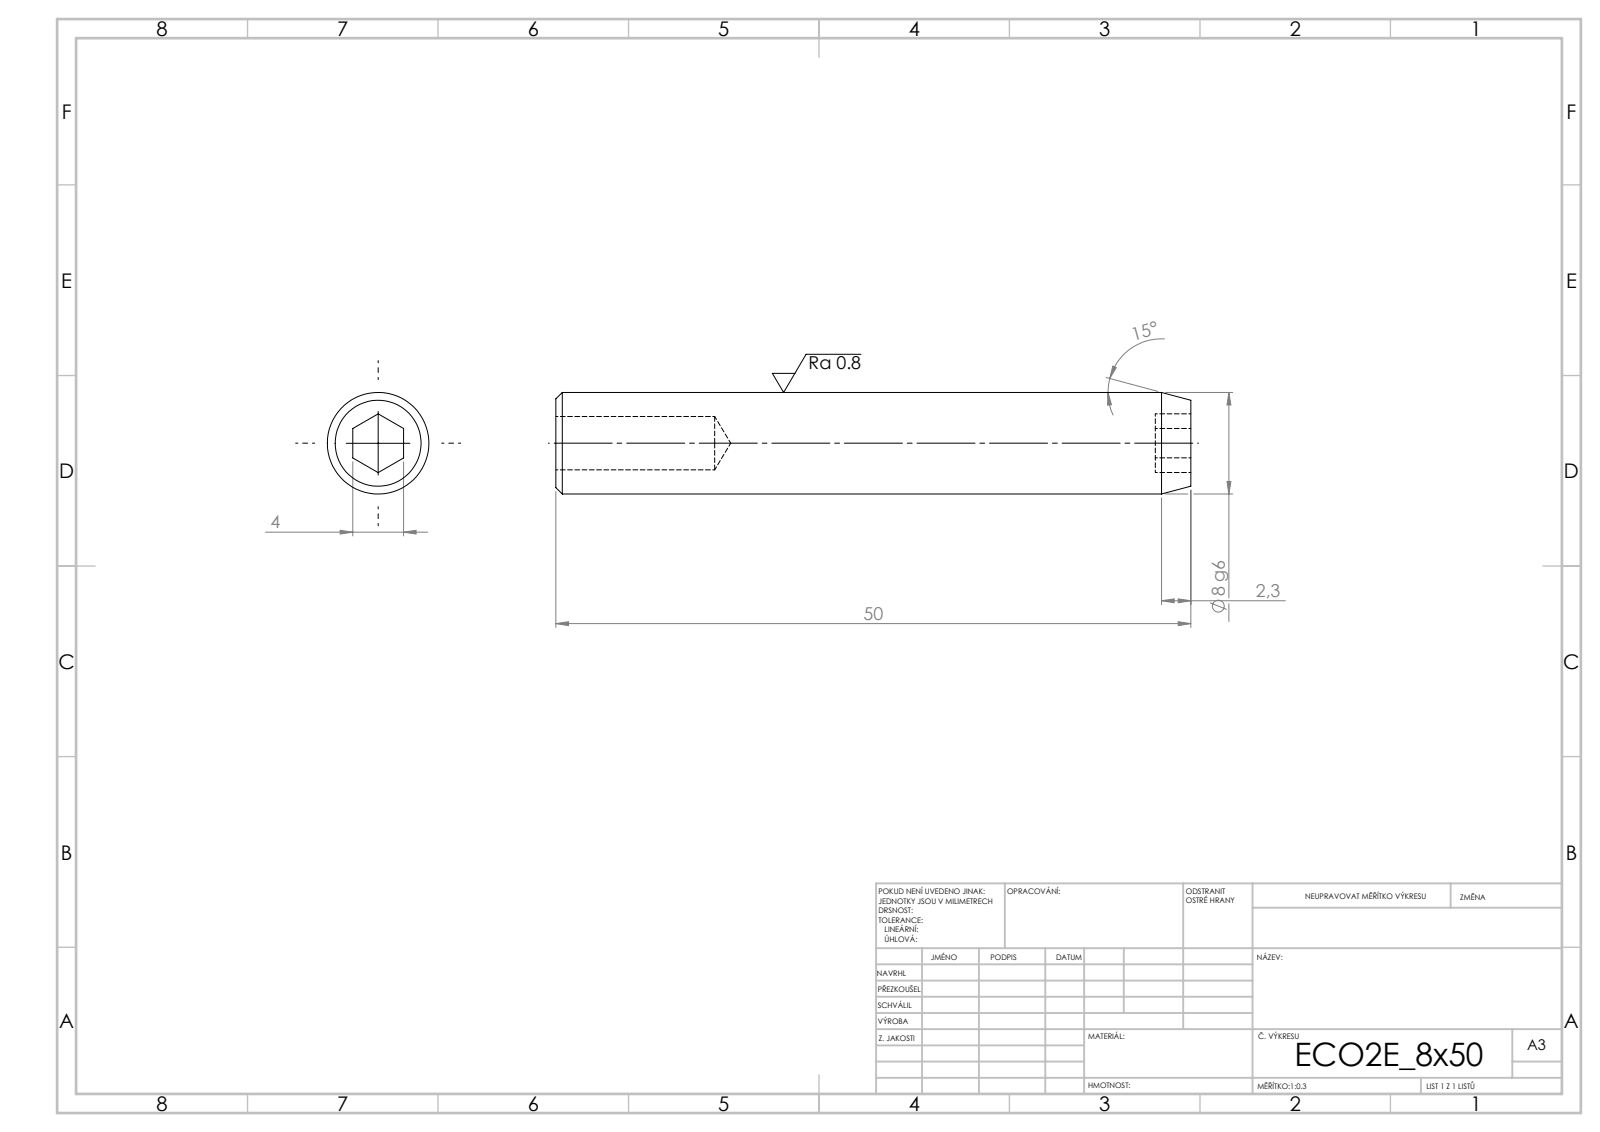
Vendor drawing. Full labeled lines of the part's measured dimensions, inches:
STEP written by: SolidWorks 2019 (CONFIG_CONTROL_DESIGN)
Units: inches
Bodies: 1 solid, 19 faces (9 planar, 4 cylindrical, 6 other)
Overall size (bounding box): 1.969 × 0.315 × 0.315
Volume: 0.139 in³ · Surface area: 2.385 in²
Round holes (diameter × count): ⌀0.165 ×1
Round bosses / shafts (diameter × count): ⌀0.315 ×1
Main face-to-face distances: 1.969, 0.157, 0.11, 1.858
